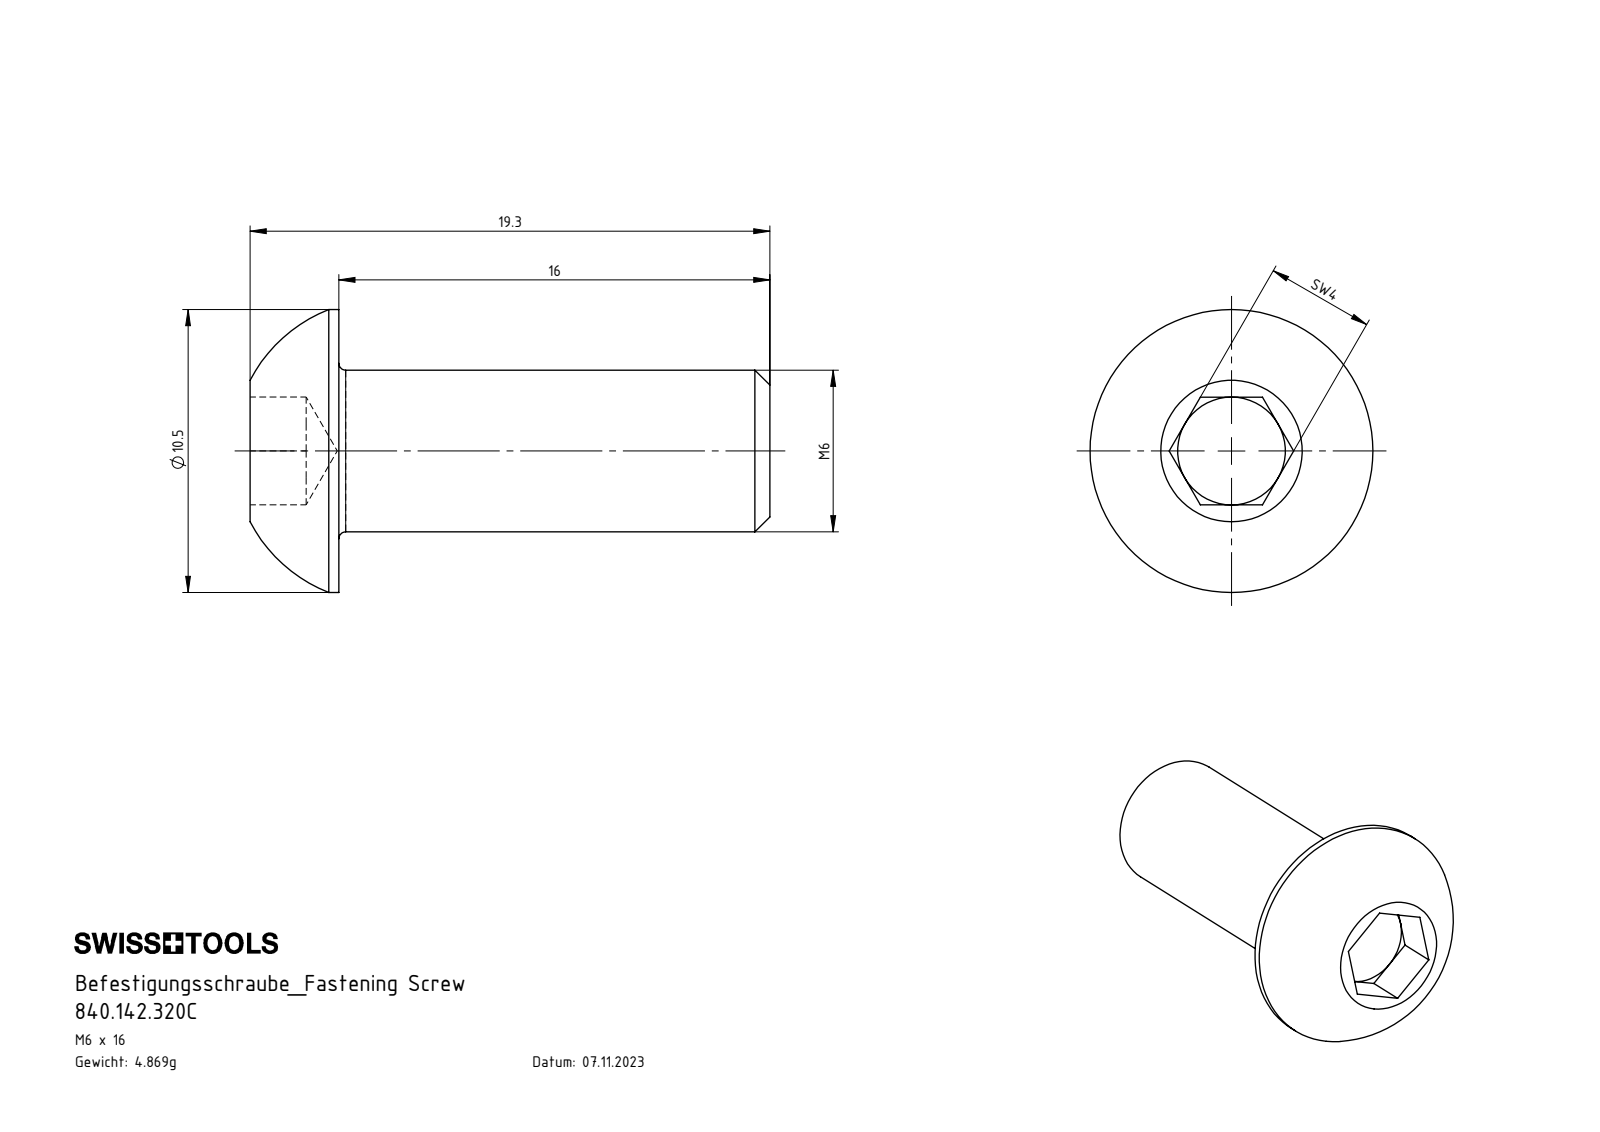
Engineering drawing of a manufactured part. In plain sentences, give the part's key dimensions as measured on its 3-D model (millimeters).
The part is named "840.142.320C". Its 3-D file was written by "SolidWorks 2022 (AUTOMOTIVE_DESIGN)". It is 1 solid with 27 faces: 15 planar, 4 cylindrical and 8 other. Overall it measures 19.3 by 10.5 by 10.5 millimeters. Its volume is 620 cubic millimeters and its surface area 548 square millimeters. Round bosses or shafts: 1 of diameter 10.5, 1 of diameter 6. The main face-to-face distances are 16, 4, 3.3, 19.3, 2.08, 1.22, 17.22.
